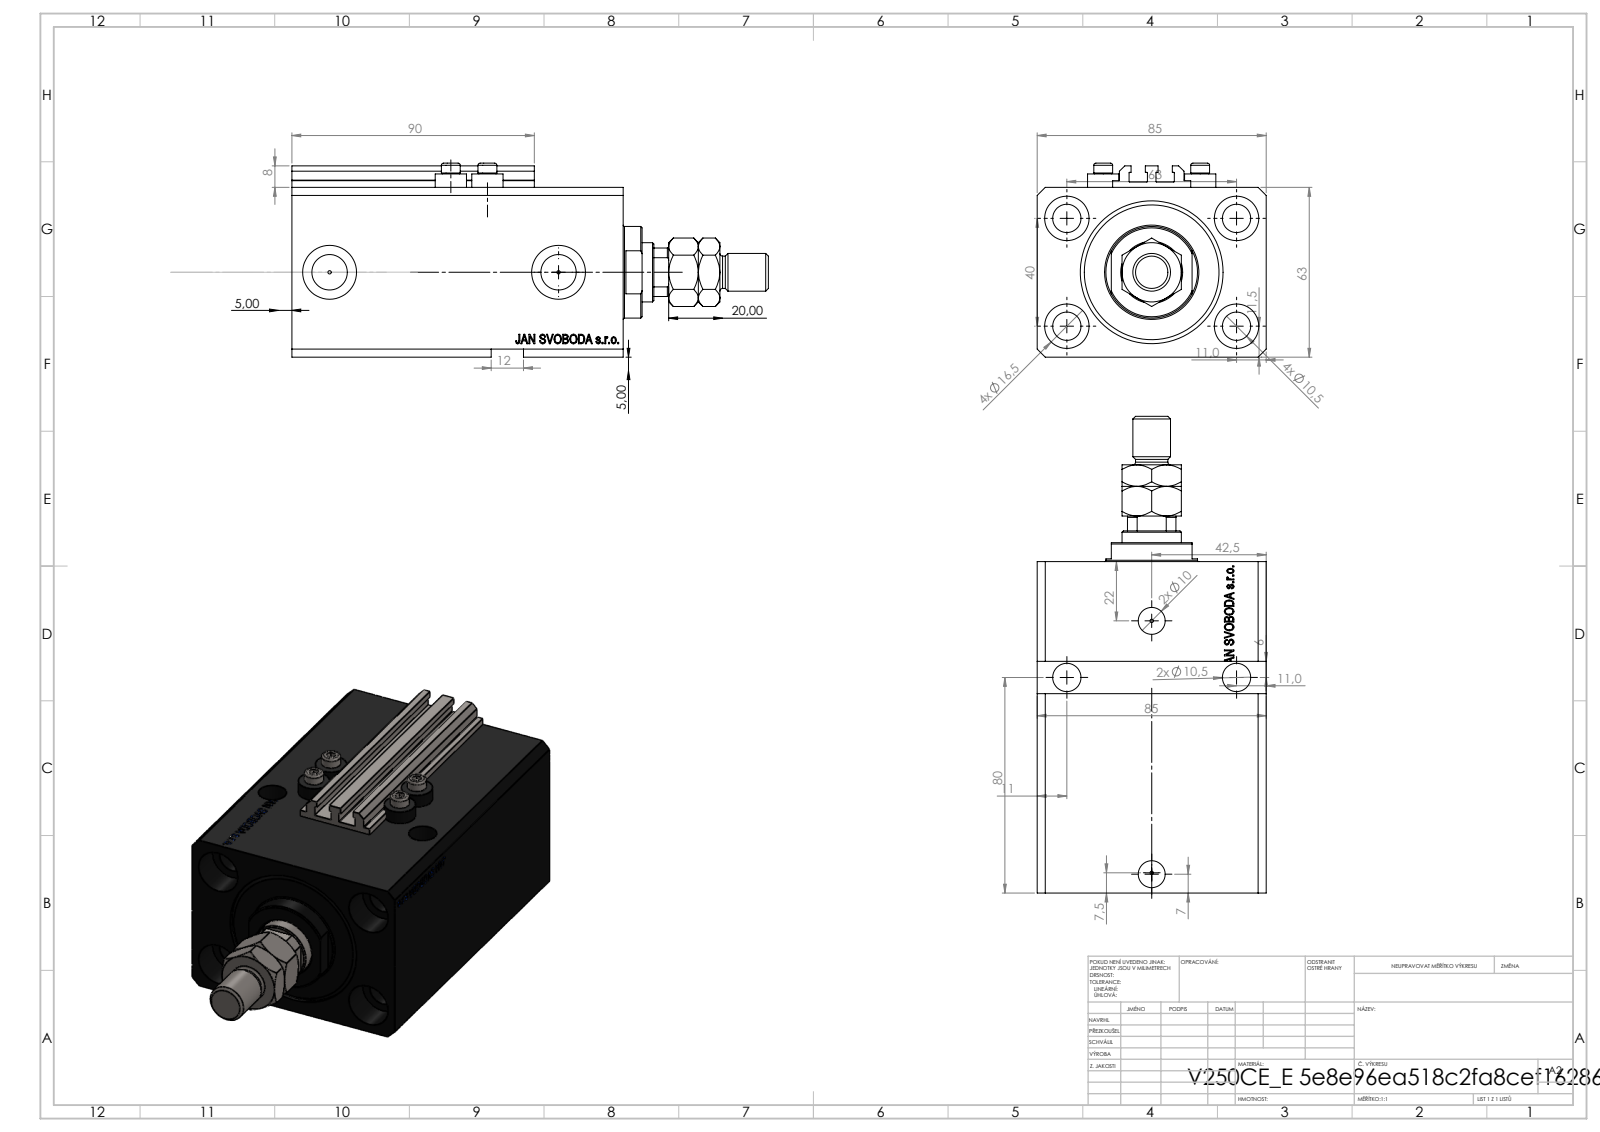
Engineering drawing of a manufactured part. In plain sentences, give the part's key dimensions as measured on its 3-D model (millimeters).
The part is named "ALLEN BOLT V250CE; V250CE_C_VCP; V250CE_VC_E; MTA (+1 more)". Its 3-D file was written by "SolidWorks 2019 (CONFIG_CONTROL_DESIGN)". It is 9 solids with 1156 faces: 550 planar, 150 cylindrical and 456 other. Overall it measures 177 by 85 by 72 millimeters. Its volume is 567 178 cubic millimeters and its surface area 122 369 square millimeters. Round holes: 8 of diameter 10.5, 4 of diameter 1.25, 4 of diameter 4, 4 of diameter 16.5, 2 of diameter 10, 2 of diameter 13.16, 2 of diameter 20, 1 of diameter 12.5, 1 of diameter 22, 1 of diameter 40, 1 of diameter 53. Round bosses or shafts: 4 of diameter 11.6, 4 of diameter 7, 1 of diameter 34, 1 of diameter 14, 1 of diameter 12. Partial cylindrical surfaces (rounded edges, fillets, slot ends): 10 of radius 0.2, 1 of radius 10.5. The main face-to-face distances are 63, 85, 17, 123, 106, 11.4, 94.6, 111.6, 3, 65. The hole center spacings are 37.31, 63, 13.6, 15.4, 24.96, 27.54, 33.62, 36.
